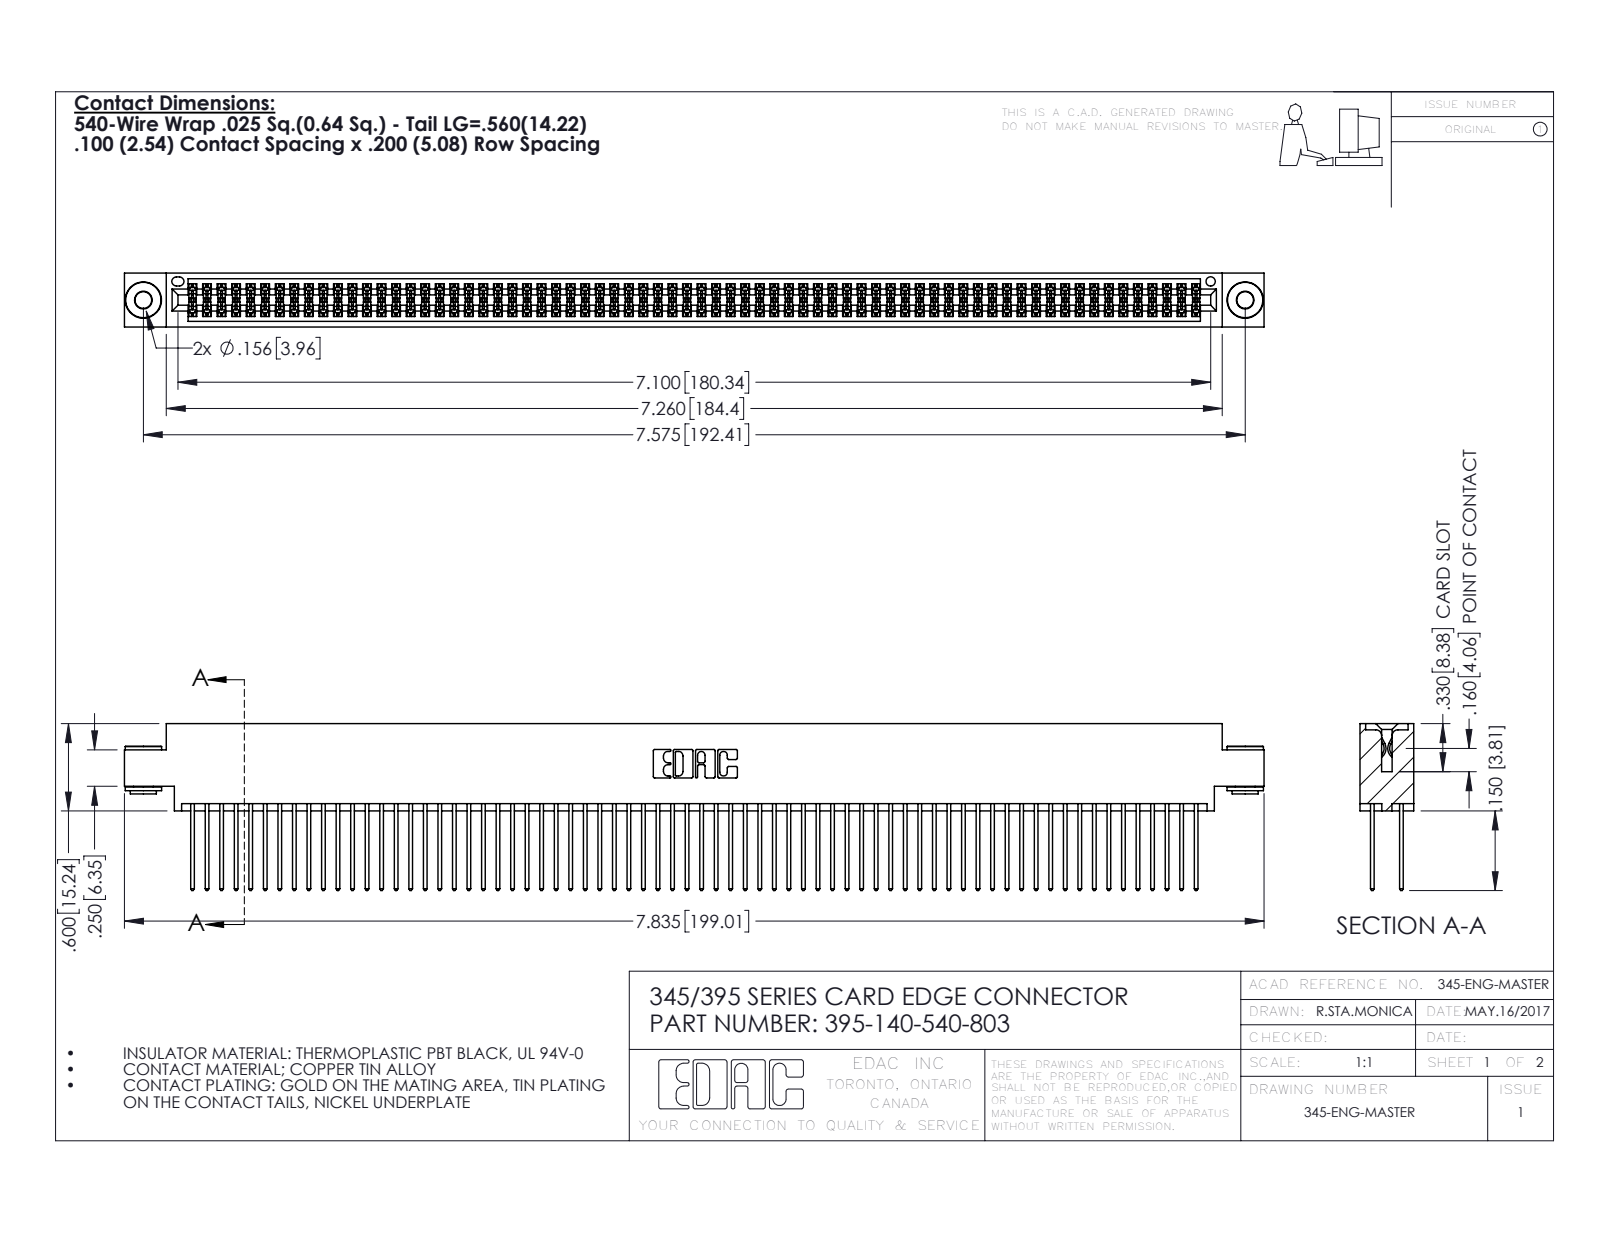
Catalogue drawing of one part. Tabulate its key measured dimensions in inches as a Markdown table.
| quantity | value |
| --- | --- |
| part name | 345 Part_0.170 Offset - 0.156 Dia-TH; 345-250-002_345-250-002-102; 345-292-001_345-293-140; 395-140-540-803 |
| STEP written by | SolidWorks 2016 (CONFIG_CONTROL_DESIGN) |
| units | inches |
| bodies | 143 solids, 7168 faces (4714 planar, 2446 cylindrical, 8 other) |
| overall size | 7.835 × 1.147 × 0.37 |
| volume | 1.222 in³ |
| surface area | 51.09 in² |
| round holes (diameter × count) | 0.116 × 2, 0.156 × 2, 0.064 × 1 |
| round bosses / shafts (diameter × count) | 0.25 × 2, 0.18 × 2, 0.136 × 2 |
| partial cylindrical surfaces (radius × count) | 0.006 × 210, 0.01 × 140, 0.01 × 22, 0.007 × 6, 0.031 × 6, 0.026 × 3, 0.014 × 2, 0.019 × 2 |
| main face-to-face distances | 0.072, 0.298, 0.2, 0.098, 0.272, 0.025, 0.37, 0.225, 0.175, 0.149 |
| hole center spacings | 0.27, 7.339, 7.575 |
